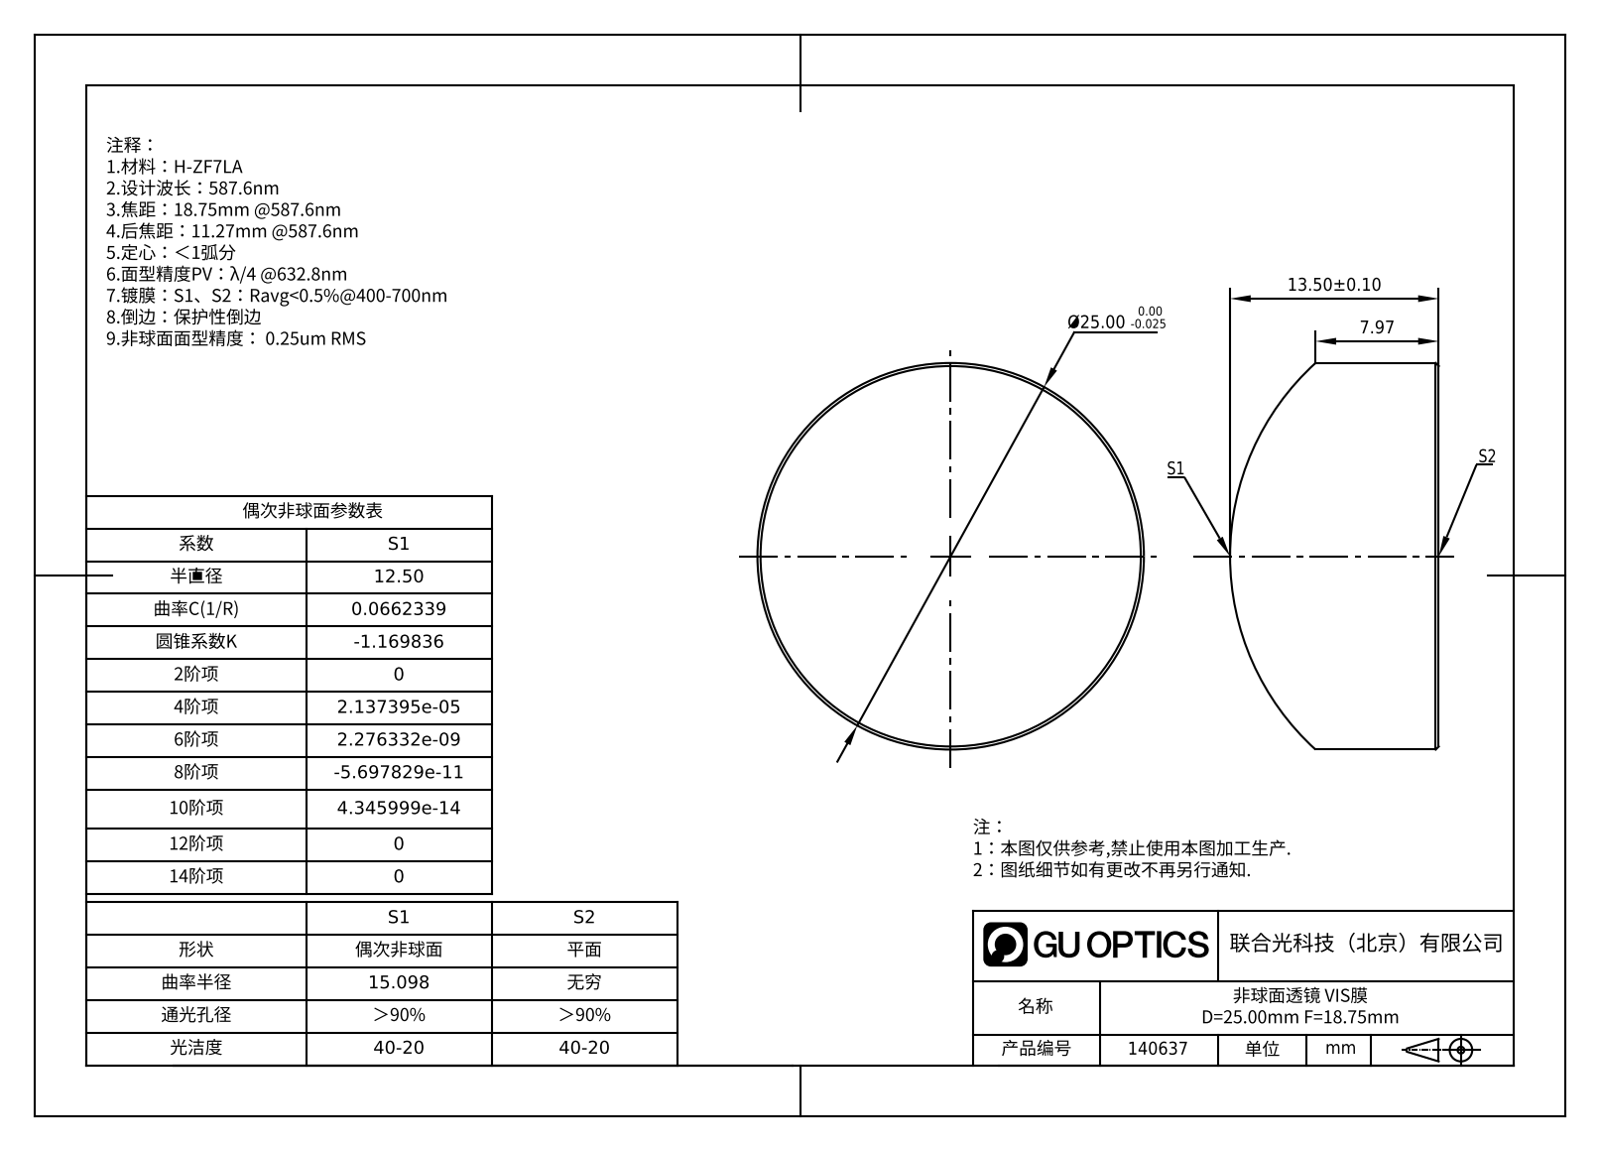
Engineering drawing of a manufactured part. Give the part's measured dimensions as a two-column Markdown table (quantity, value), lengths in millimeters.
| quantity | value |
| --- | --- |
| part name | GLA11-025-18.75-H-VIS |
| STEP written by | SolidWorks 2022 (AUTOMOTIVE_DESIGN) |
| units | millimeters |
| bodies | 1 solid, 7 faces (1 planar, 2 cylindrical, 4 other) |
| overall size | 25 × 25 × 13.5 |
| volume | 5 357 mm³ |
| surface area | 1 695 mm² |
| round bosses / shafts (diameter × count) | 25 × 1 |
